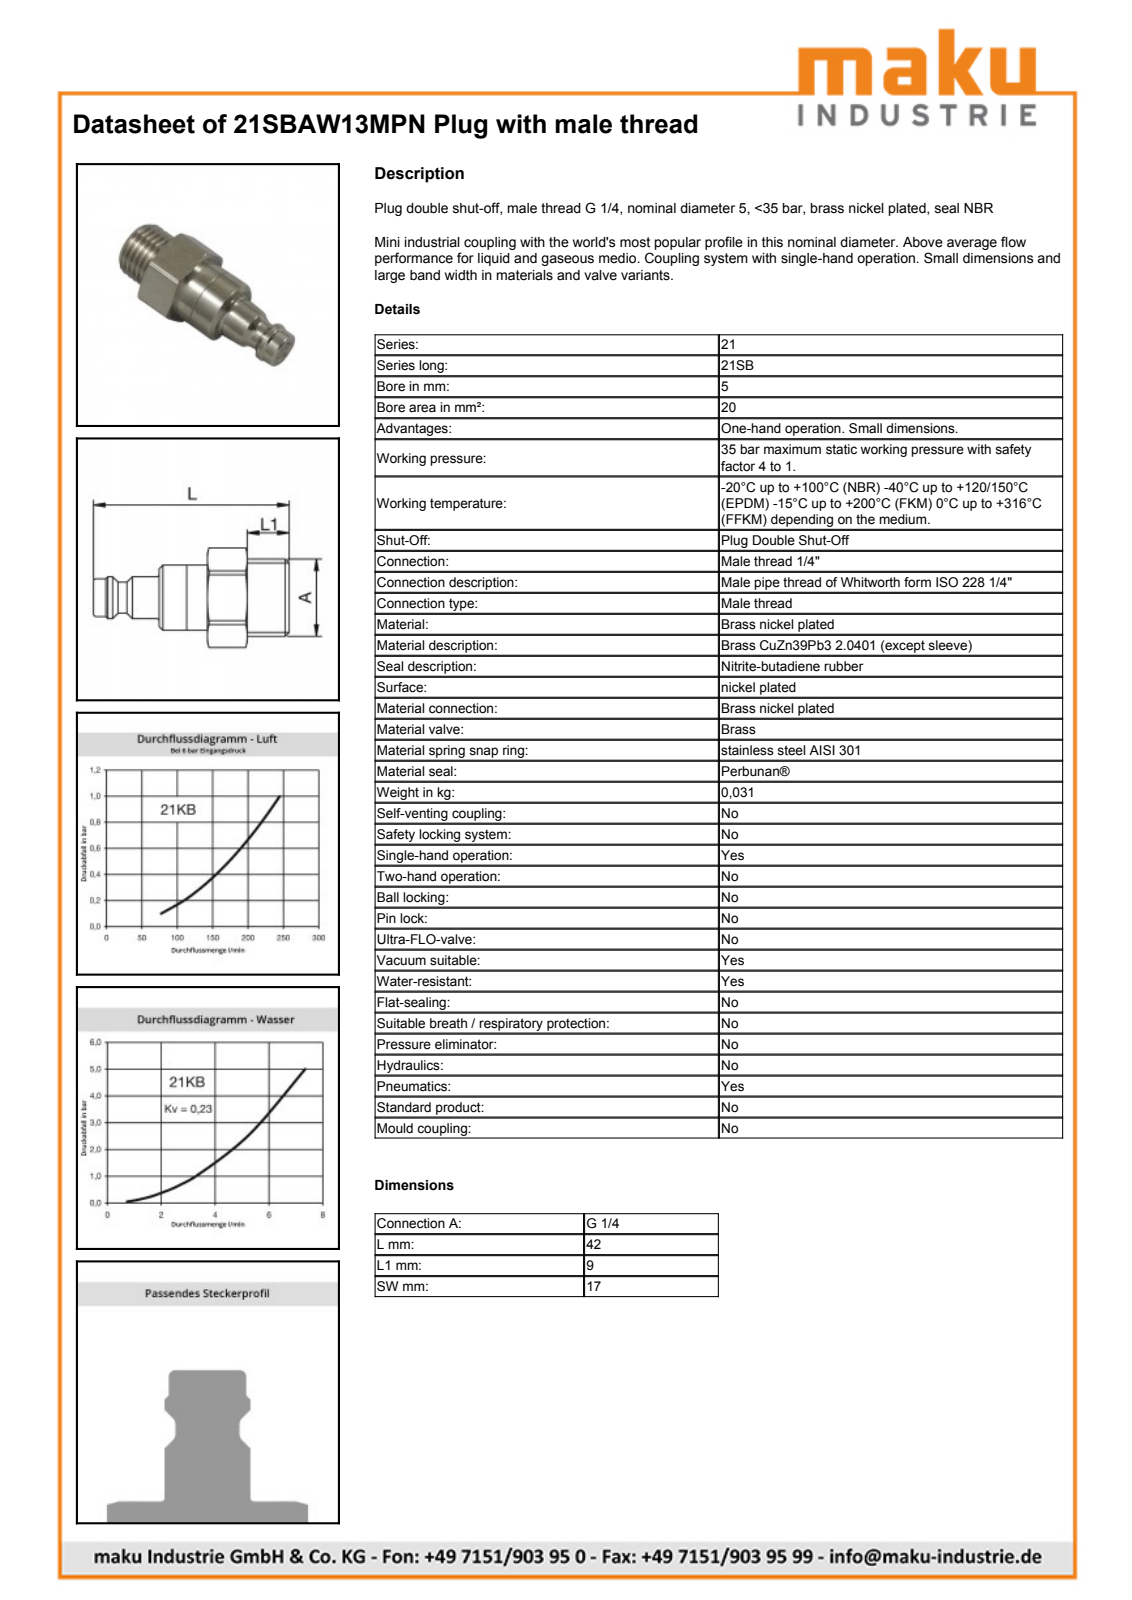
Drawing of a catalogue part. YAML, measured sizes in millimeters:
part_name: "D107131"
step_written_by: "Autodesk Inventor 2013 (AUTOMOTIVE_DESIGN)"
units: millimeters
bodies: {solids: 1, faces: 53, planar: 12, cylindrical: 16, other: 25}
overall_size: [42, 19.15, 17.14]
volume: 5672
surface_area: 2331
round_holes:
  - {diameter: 11.46, count: 1}
round_bosses_or_shafts:
  - {diameter: 14, count: 1}
  - {diameter: 13.16, count: 1}
  - {diameter: 11, count: 1}
  - {diameter: 10.88, count: 1}
  - {diameter: 9, count: 1}
  - {diameter: 8.1, count: 1}
  - {diameter: 6.65, count: 1}
partial_cylinders:
  - {radius: 9.57, count: 1}
face_to_face_distances: [17, 9, 8.55, 17.55, 10.35, 18.9, 27.9, 14.1, 24.45, 33]
